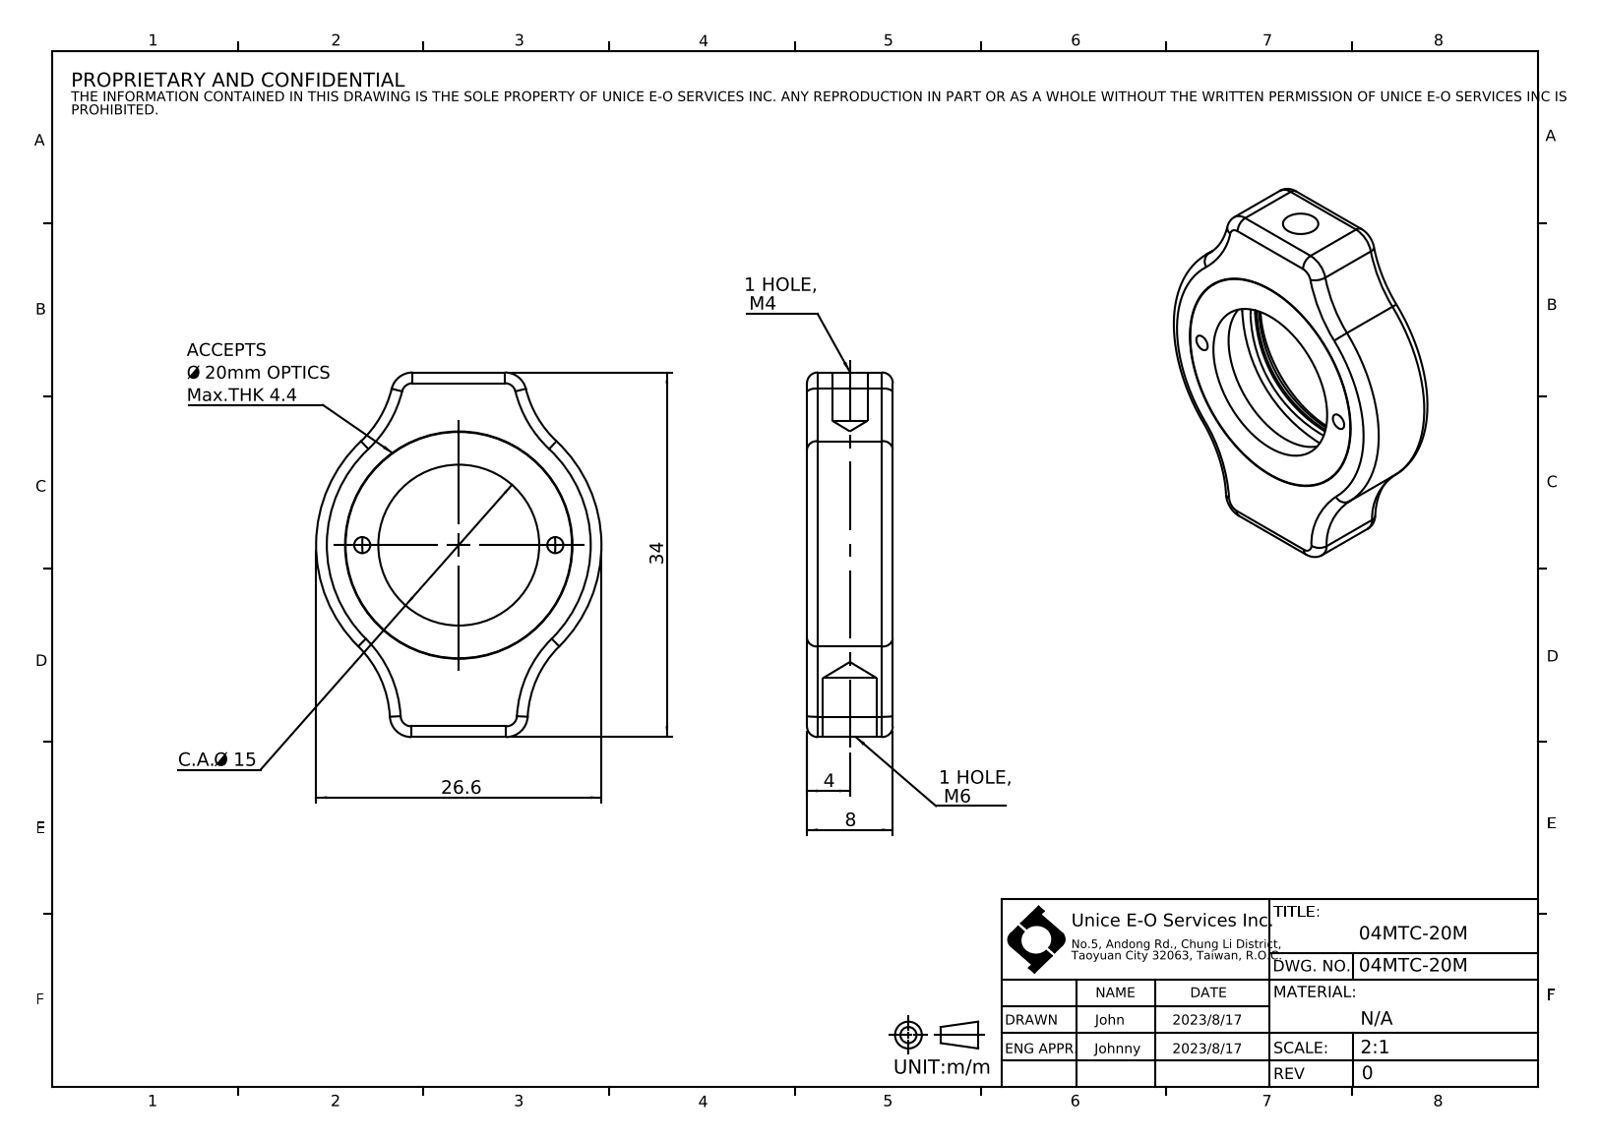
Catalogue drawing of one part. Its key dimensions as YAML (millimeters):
part_name: "04MTC-20M"
step_written_by: "SolidWorks 2016 (CONFIG_CONTROL_DESIGN)"
units: millimeters
bodies: {solids: 3, faces: 78, planar: 9, cylindrical: 35, other: 34}
overall_size: [34, 26.6, 8]
volume: 3029
surface_area: 2918
round_holes:
  - {diameter: 1.5, count: 2}
  - {diameter: 3.3, count: 1}
  - {diameter: 5, count: 1}
  - {diameter: 15, count: 1}
  - {diameter: 18, count: 1}
  - {diameter: 20.2, count: 1}
round_bosses_or_shafts:
  - {diameter: 21.1, count: 1}
partial_cylinders:
  - {radius: 1, count: 4}
  - {radius: 2, count: 4}
  - {radius: 10, count: 4}
  - {radius: 13.3, count: 1}
face_to_face_distances: [8, 2, 6, 7, 5, 1, 6.4, 4.4, 0.6, 1.6]
hole_center_spacings: [9, 18]
